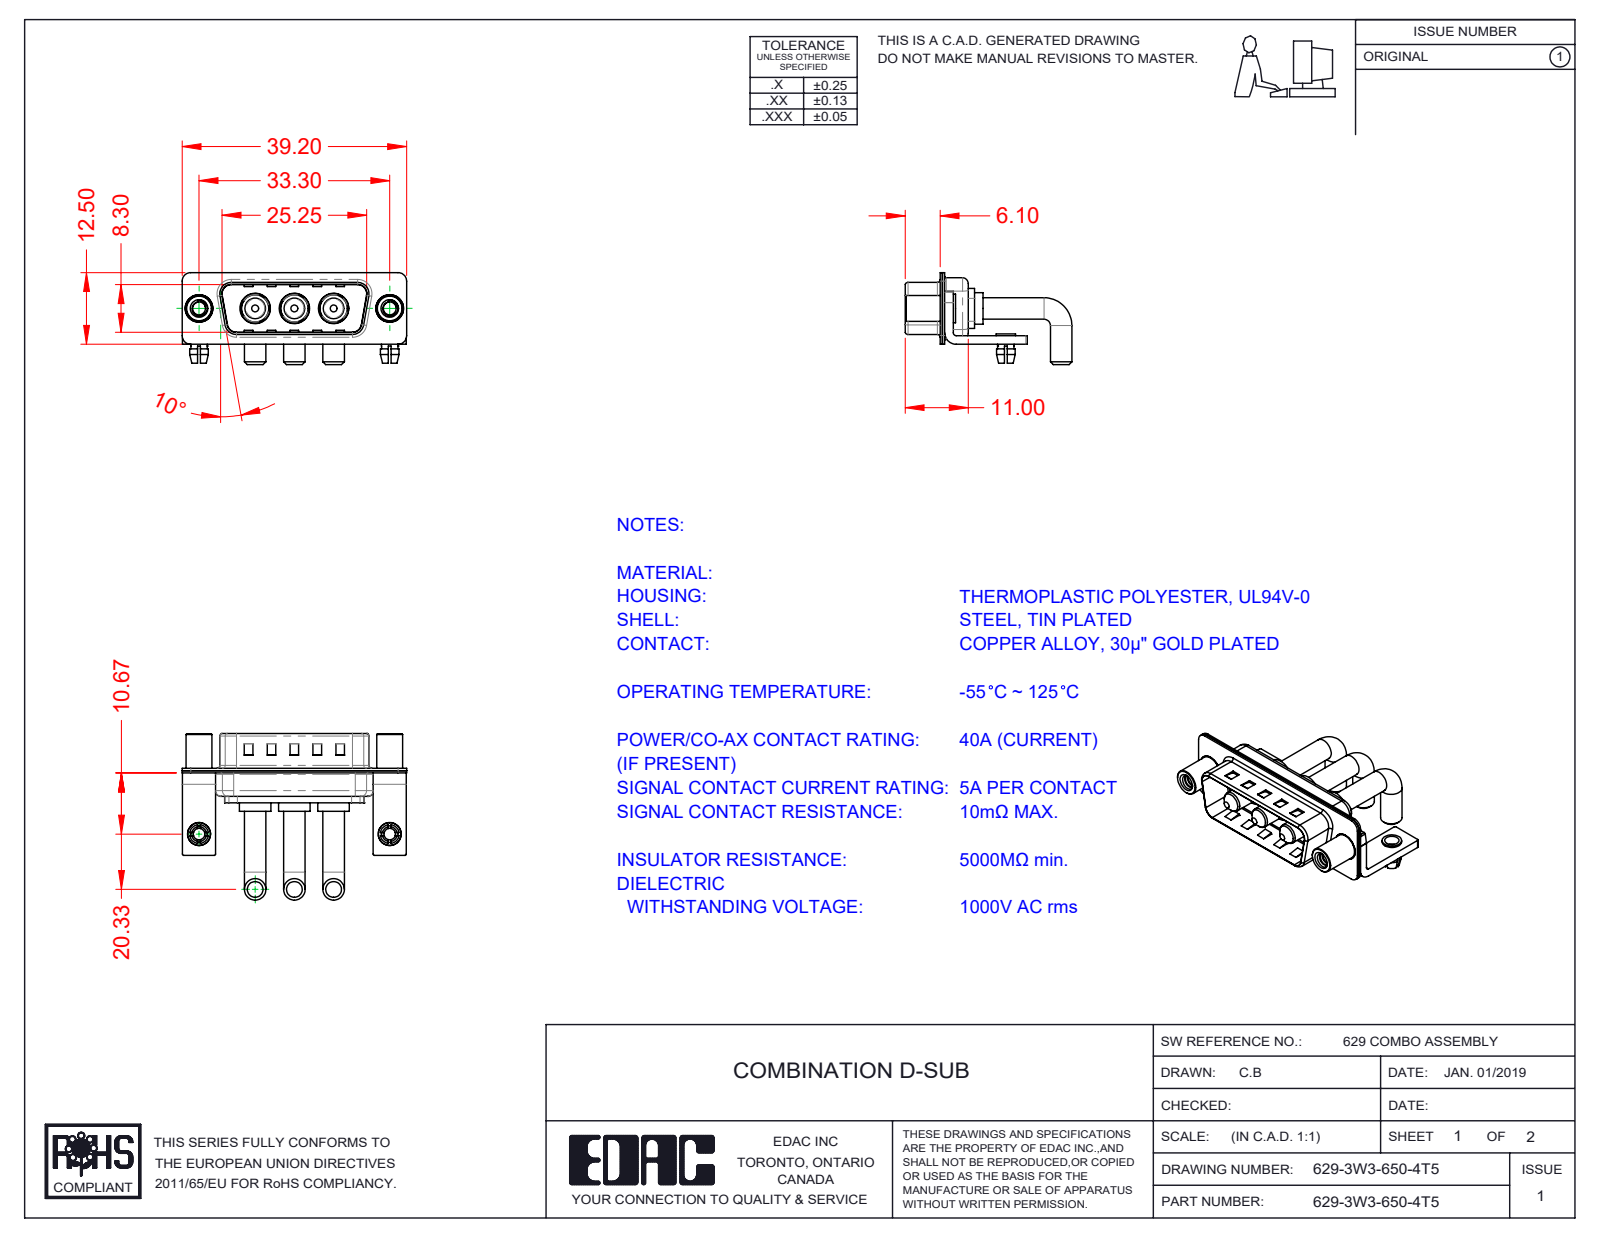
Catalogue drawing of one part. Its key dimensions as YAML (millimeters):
part_name: "629-3W3-650-4T5; Power Pin_Ext 40A RA; 629Combo Housing_3W3; 629Combo Board Lock (+4 more)"
step_written_by: "SolidWorks 2020 (CONFIG_CONTROL_DESIGN)"
units: millimeters
bodies: {solids: 15, faces: 649, planar: 239, cylindrical: 288, other: 122}
overall_size: [39.2, 29.11, 16.05]
volume: 3140
surface_area: 6498
round_holes:
  - {diameter: 4.85, count: 3}
  - {diameter: 5.3, count: 3}
  - {diameter: 2, count: 2}
  - {diameter: 2.26, count: 2}
  - {diameter: 2.5, count: 2}
  - {diameter: 3.2, count: 2}
  - {diameter: 4, count: 2}
  - {diameter: 4.8, count: 2}
round_bosses_or_shafts:
  - {diameter: 3.75, count: 6}
  - {diameter: 5.5, count: 3}
  - {diameter: 5.2, count: 3}
  - {diameter: 4.75, count: 3}
  - {diameter: 3.6, count: 3}
  - {diameter: 5, count: 2}
  - {diameter: 4.9, count: 2}
  - {diameter: 4.5, count: 2}
partial_cylinders:
  - {radius: 0.25, count: 16}
  - {radius: 1.5, count: 16}
  - {radius: 2, count: 13}
  - {radius: 0.5, count: 9}
  - {radius: 1.6, count: 8}
  - {radius: 0.6, count: 4}
  - {radius: 0.65, count: 4}
  - {radius: 0.9, count: 4}
face_to_face_distances: [0.4, 0.8, 1.5, 9.5, 8.7, 9.1, 9.9, 5.2, 0.75, 0.6]
hole_center_spacings: [6.85, 9.8, 16.65, 23.5, 33.3, 13.7]
